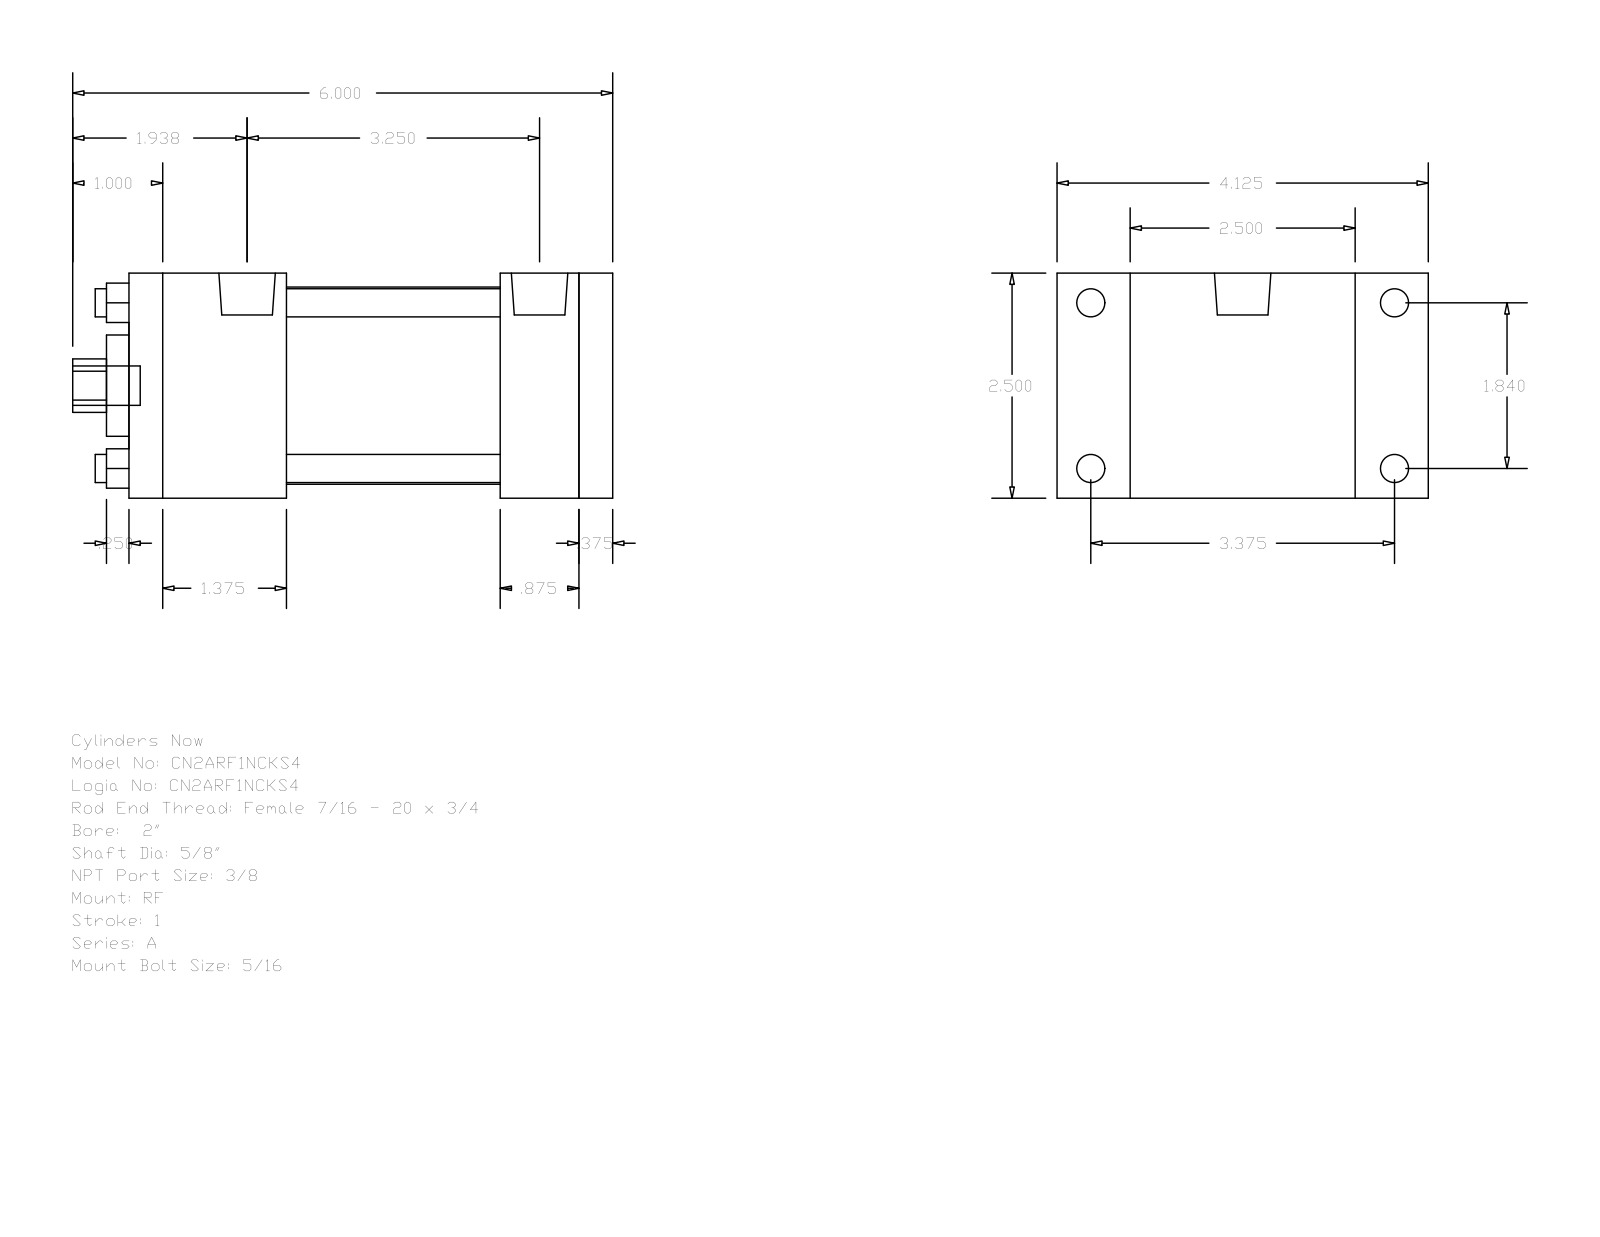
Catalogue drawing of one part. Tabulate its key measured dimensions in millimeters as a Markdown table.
| quantity | value |
| --- | --- |
| part name | A_RF__0200_0.625 |
| STEP written by | GSSL Pune (CONFIG_CONTROL_DESIGN) |
| units | millimeters |
| bodies | 0 solids, 92 faces (64 planar, 28 cylindrical, 0 other) |
| overall size | 152.4 × 104.78 × 63.5 |
| round holes (diameter × count) | 7.94 × 4, 15.88 × 1, 28.57 × 1, 55.63 × 1 |
| round bosses / shafts (diameter × count) | 7.94 × 4, 5.56 × 4, 15.93 × 2, 11.11 × 1 |
| partial cylindrical surfaces (radius × count) | 7.54 × 1 |
| main face-to-face distances | 63.5, 136.52, 9.52, 127, 44.45, 82.55, 92.07, 104.77, 60.32, 22.23 |
| hole center spacings | 33.05, 46.74, 66.1 |
